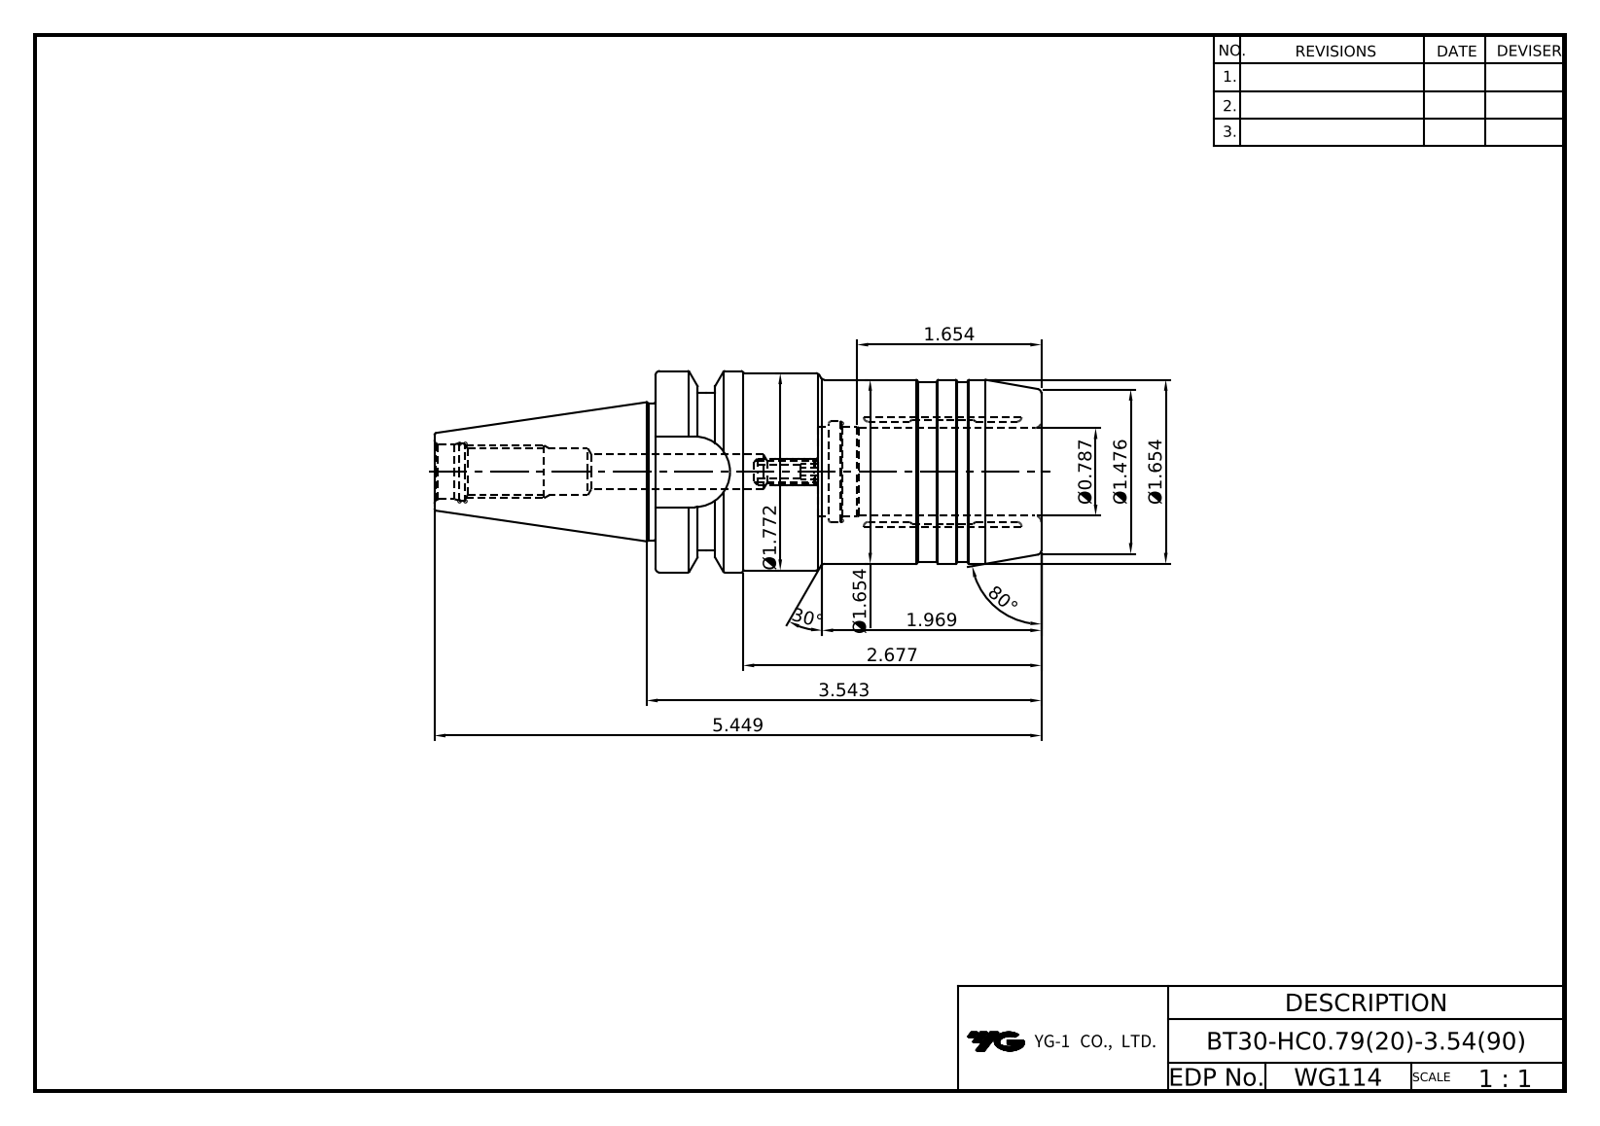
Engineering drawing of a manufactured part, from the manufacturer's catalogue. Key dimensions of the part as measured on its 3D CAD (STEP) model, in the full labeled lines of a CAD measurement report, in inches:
Part name (STEP PRODUCT): LO-BT30ADB-HC20-90
STEP written by: Autodesk Inventor 2022 (AUTOMOTIVE_DESIGN)
Units: inches
Bodies: 1 solid, 95 faces (20 planar, 39 cylindrical, 36 other)
Overall size (bounding box): 5.449 × 1.811 × 1.811
Volume: 7.672 in³ · Surface area: 38.81 in²
Round holes (diameter × count): ⌀0.128 ×4, ⌀0.157 ×4, ⌀0.194 ×1, ⌀0.315 ×1, ⌀0.398 ×1, ⌀0.492 ×1, ⌀0.516 ×1, ⌀0.787 ×1, ⌀0.811 ×1
Round bosses / shafts (diameter × count): ⌀1.811 ×1, ⌀1.752 ×1, ⌀1.654 ×1, ⌀1.614 ×1, ⌀1.228 ×1
Partial cylindrical surfaces — rounded edges, fillets, slot ends (radius × count): R0.317 ×1, R0.709 ×1
Main face-to-face distances: 3.465, 1.457, 2.008, 1.283, 0.535, 0.921, 2.929, 0.378, 0.157, 1.079
